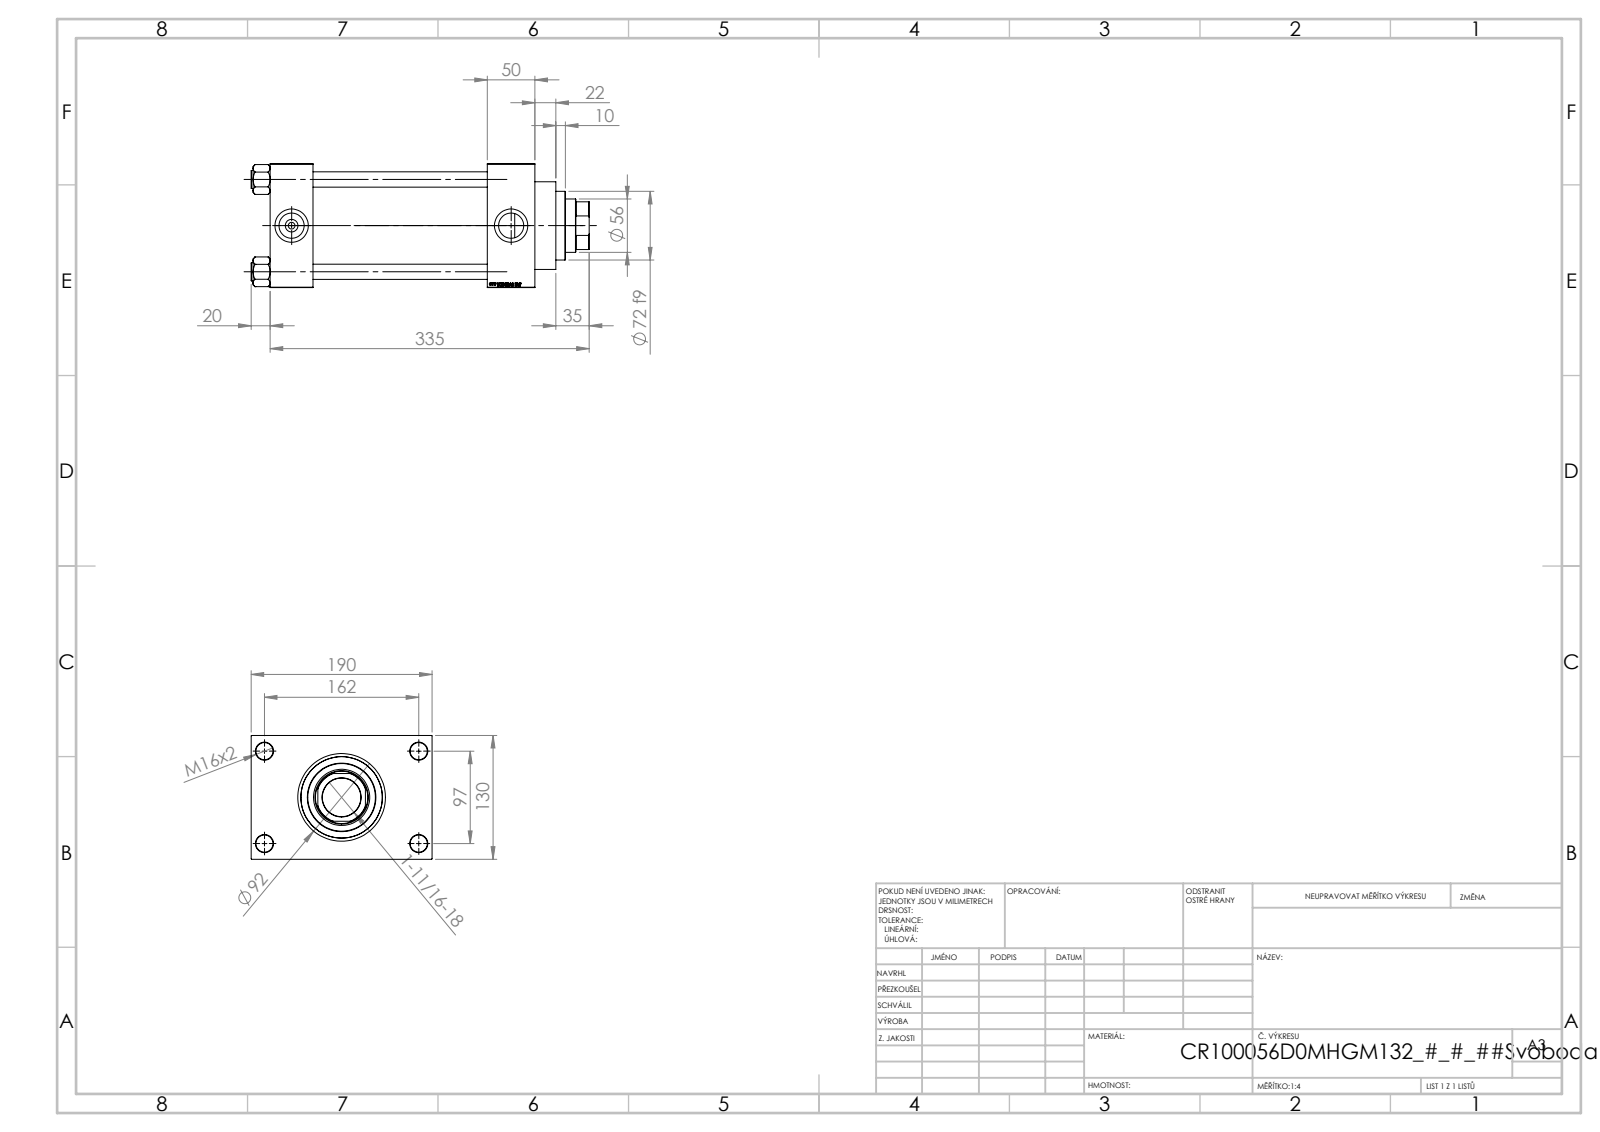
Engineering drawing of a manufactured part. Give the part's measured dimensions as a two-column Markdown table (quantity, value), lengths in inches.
| quantity | value |
| --- | --- |
| part name | V215CR_VCP_D; V215CR_D_Body; V215_VC_A; NUT_M5_D (+1 more) |
| STEP written by | SolidWorks 2019 (CONFIG_CONTROL_DESIGN) |
| units | inches |
| bodies | 11 solids, 1151 faces (545 planar, 88 cylindrical, 518 other) |
| overall size | 13.976 × 7.48 × 5.118 |
| volume | 189.4 in³ |
| surface area | 739.5 in² |
| round holes (diameter × count) | 0.63 × 4, 0.709 × 4, 0.276 × 2, 1.041 × 2, 1.378 × 2, 1.594 × 1, 2.205 × 1, 2.323 × 1, 2.992 × 1, 3.366 × 1, 3.937 × 1 |
| round bosses / shafts (diameter × count) | 0.748 × 4, 4.173 × 1, 3.622 × 1, 2.835 × 1 |
| partial cylindrical surfaces (radius × count) | 1.063 × 1 |
| main face-to-face distances | 5.118, 1.969, 1.772, 7.205, 8.976, 10.945, 9.173, 1.181, 6.299, 7.48 |
| hole center spacings | 1.281, 2.698, 3.717, 3.815, 4.026, 5.096, 6.367, 3.819 |
